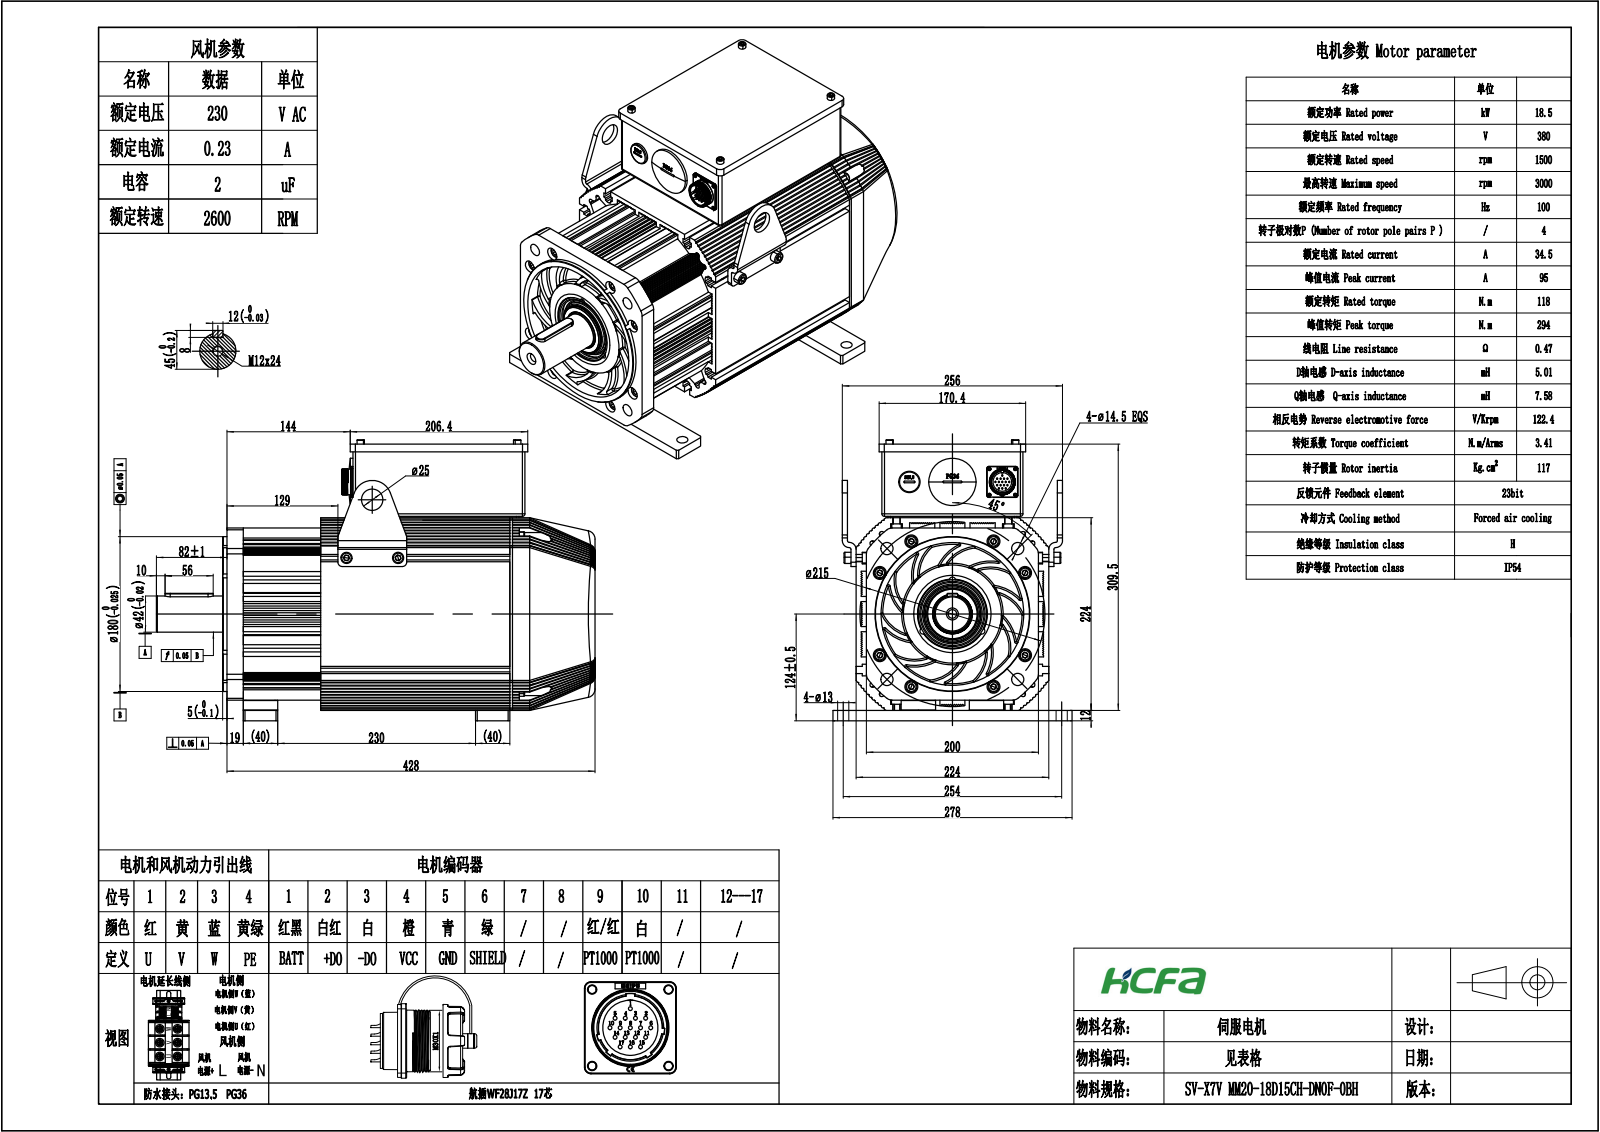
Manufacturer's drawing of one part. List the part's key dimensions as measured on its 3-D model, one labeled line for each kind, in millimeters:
Part name (STEP PRODUCT): 10002030101-0033-SV-X7VMM20-18D15CH-DN0F-0BH-5段外形图
STEP written by: SolidWorks 2021 (CONFIG_CONTROL_DESIGN)
Units: millimetres
Bodies: 8 solids, 3616 faces (1495 planar, 1193 cylindrical, 928 other)
Overall size (bounding box): 510 × 326.5 × 278
Volume: 17 970 000 mm³ · Surface area: 1 065 000 mm²
Round holes (diameter × count): ⌀9 ×22, ⌀15 ×14, ⌀13 ×8, ⌀2.5 ×4, ⌀5 ×4, ⌀6.8 ×4, ⌀7 ×4, ⌀10 ×4, ⌀14.5 ×4, ⌀10.2 ×1, ⌀20.5 ×1, ⌀21.7 ×1
Round bosses / shafts (diameter × count): ⌀8 ×20, ⌀1.5 ×17, ⌀13 ×16, ⌀10 ×4, ⌀8.5 ×4, ⌀6.3 ×4, ⌀6 ×4, ⌀40 ×2
Partial cylindrical surfaces — rounded edges, fillets, slot ends (radius × count): R2 ×112, R1 ×22, R1.5 ×20, R5 ×18, R1.4 ×16, R3 ×12, R0.2 ×10, R10 ×10
Main face-to-face distances: 2, 224, 12, 307.5, 6, 309.5, 212, 30, 194, 32
Hole centre spacings: 29.47, 43.17, 97, 124.07, 137.18, 138.41, 162.9, 167.15
